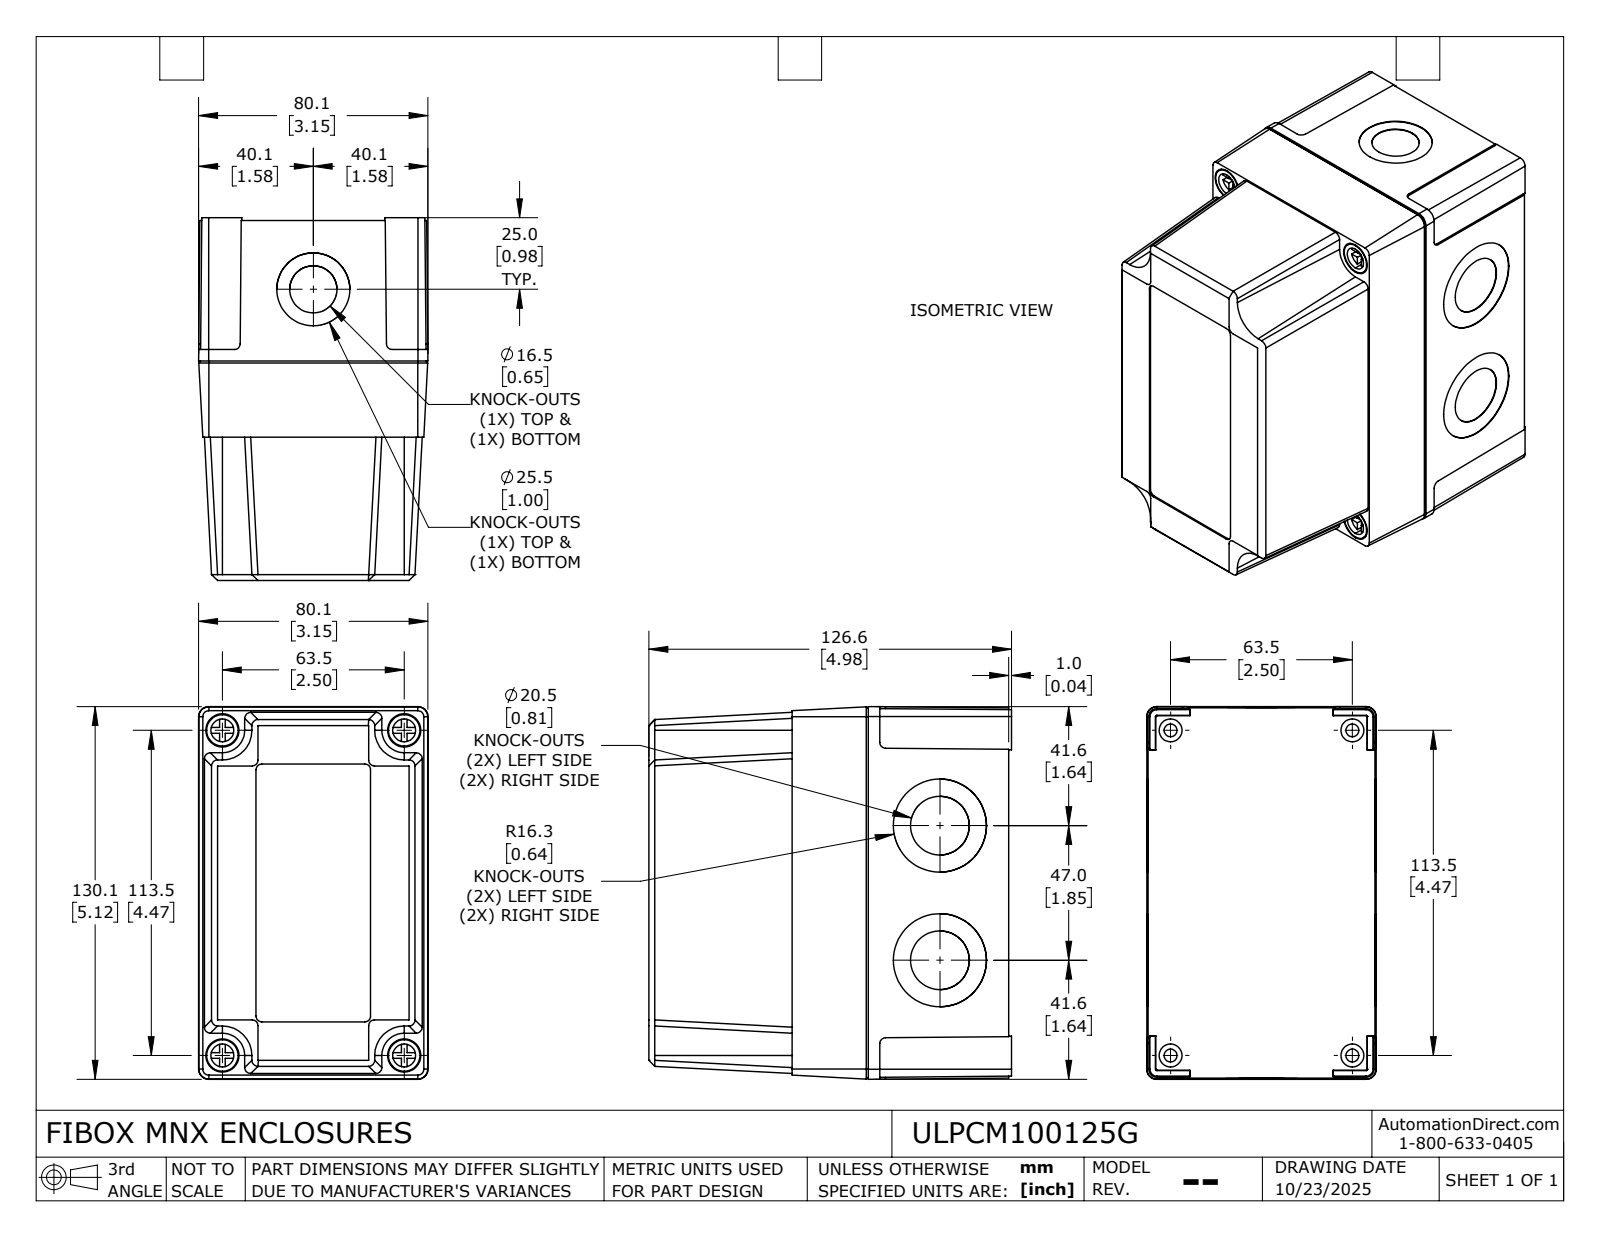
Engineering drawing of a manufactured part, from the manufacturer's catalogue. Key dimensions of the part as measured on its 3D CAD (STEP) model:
Part name (STEP PRODUCT): ULPCM100125G_Default
STEP written by: SolidWorks 2024 (CONFIG_CONTROL_DESIGN)
Units: inches
Bodies: 6 solids, 565 faces (331 planar, 184 cylindrical, 50 other)
Overall size (bounding box): 5.122 × 4.984 × 3.154
Volume: 13.27 in³ · Surface area: 231 in²
Round holes (diameter × count): ⌀0.126 ×8, ⌀0.157 ×8, ⌀0.177 ×4, ⌀0.315 ×4, ⌀0.457 ×4, ⌀0.807 ×4, ⌀1.28 ×4, ⌀0.65 ×2, ⌀1.004 ×2
Round bosses / shafts (diameter × count): ⌀0.315 ×8, ⌀0.098 ×8, ⌀0.433 ×4, ⌀0.283 ×4
Partial cylindrical surfaces — rounded edges, fillets, slot ends (radius × count): R0.079 ×8, R0.083 ×8, R0.056 ×6, R0.021 ×4, R0.197 ×4, R0.023 ×2
Main face-to-face distances: 0.055, 0.165, 0.118, 4.854, 4.736, 0.077, 0.022, 0.026, 0.139, 0.078
Hole centre spacings: 0.841, 0.888, 1.333, 1.476, 1.939, 2.159, 2.174, 2.281
